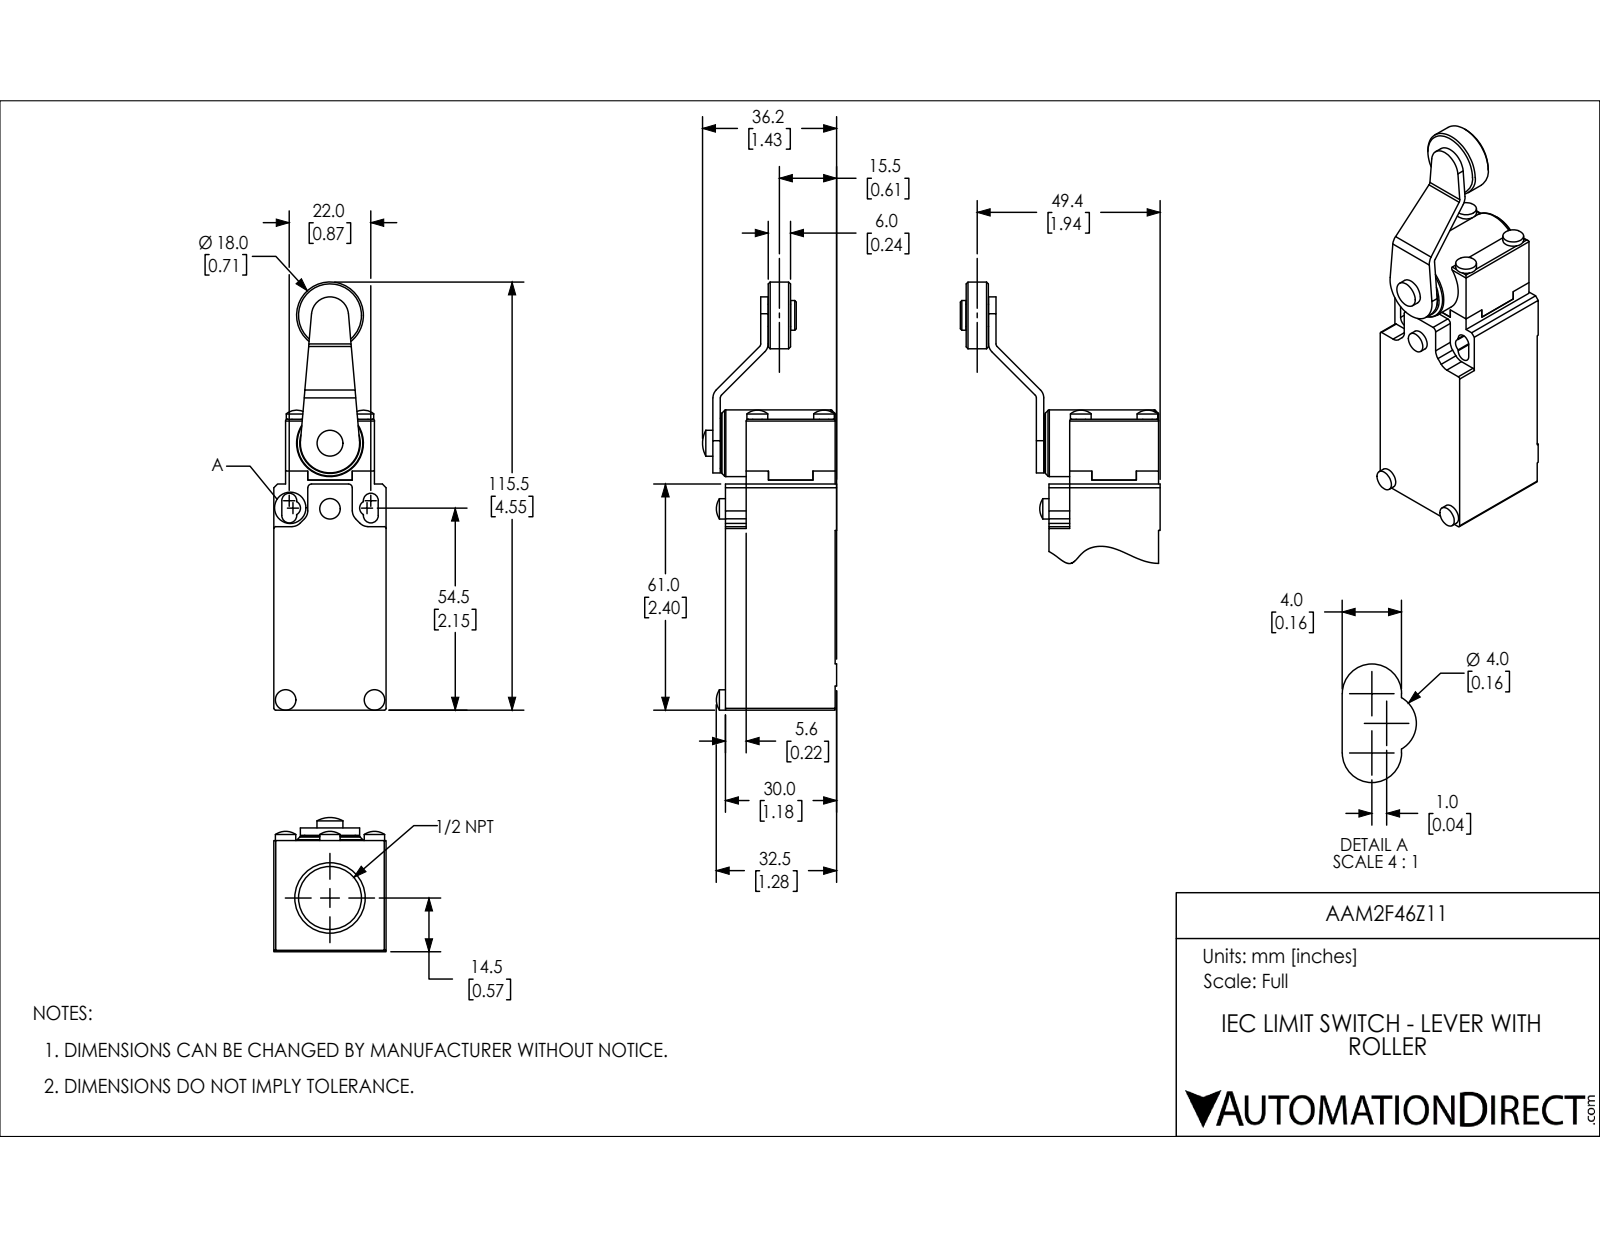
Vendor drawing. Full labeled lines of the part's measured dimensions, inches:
Part name (STEP PRODUCT): AAM2F46Z11
STEP written by: SolidWorks 2018 (AUTOMOTIVE_DESIGN)
Units: inches
Bodies: 3 solids, 218 faces (95 planar, 93 cylindrical, 30 other)
Overall size (bounding box): 4.547 × 1.425 × 1.193
Volume: 4.054 in³ · Surface area: 25.41 in²
Round holes (diameter × count): ⌀0.669 ×1, ⌀0.748 ×1
Round bosses / shafts (diameter × count): ⌀0.22 ×4, ⌀0.217 ×3, ⌀0.709 ×2, ⌀0.587 ×1, ⌀0.531 ×1, ⌀0.315 ×1, ⌀0.276 ×1, ⌀0.236 ×1
Partial cylindrical surfaces — rounded edges, fillets, slot ends (radius × count): R0.02 ×8, R0.079 ×6, R0.118 ×6, R0.039 ×4, R0.197 ×1, R0.315 ×1, R0.394 ×1, R0.4 ×1
Main face-to-face distances: 1.193, 1.165, 0.124, 1.069, 0.945, 0.236, 0.079, 1.181, 0.016, 0.276
